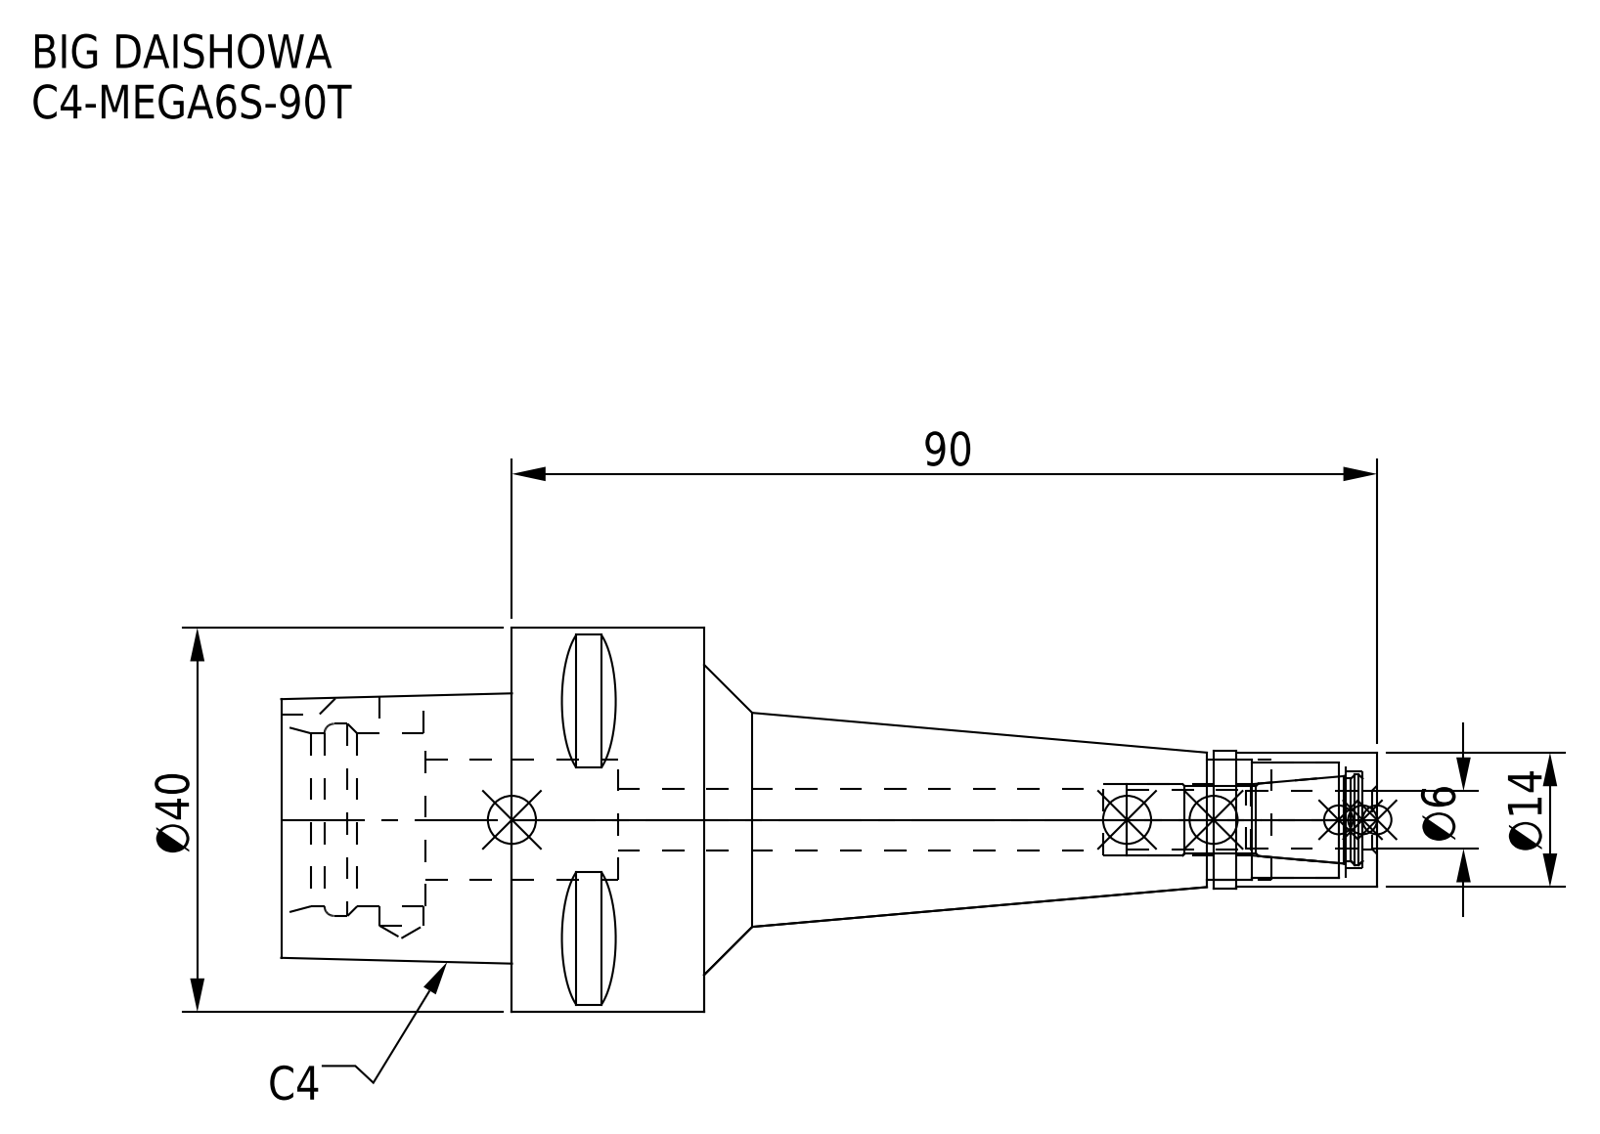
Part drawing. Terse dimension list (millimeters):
name: C4-MEGA6S-90T-060-FreeParts; C4-MEGA6S-90T; DXF_TEMP_ASSY_ASM_4_ASM.stp; C4-MEGA6S-90T-060.stp (+3 more)
written by: SolidWorks 2019 (CONFIG_CONTROL_DESIGN)
unit: mm
bodies: 2 solids, 90 faces (37 planar, 35 cylindrical, 18 other)
size: 114 × 40 × 40
volume: 47 159 mm³; area: 15 215 mm²
holes: 1× ⌀4.6, 1× ⌀6.1, 1× ⌀6.4, 1× ⌀7.4, 1× ⌀10, 1× ⌀12, 1× ⌀12.5, 1× ⌀18, 1× ⌀20
bosses: 1× ⌀40, 1× ⌀14.3, 1× ⌀14
rounds: 1× R3
face distances: 20, 9, 44, 24, 29, 15, 15.52, 99, 70, 90
